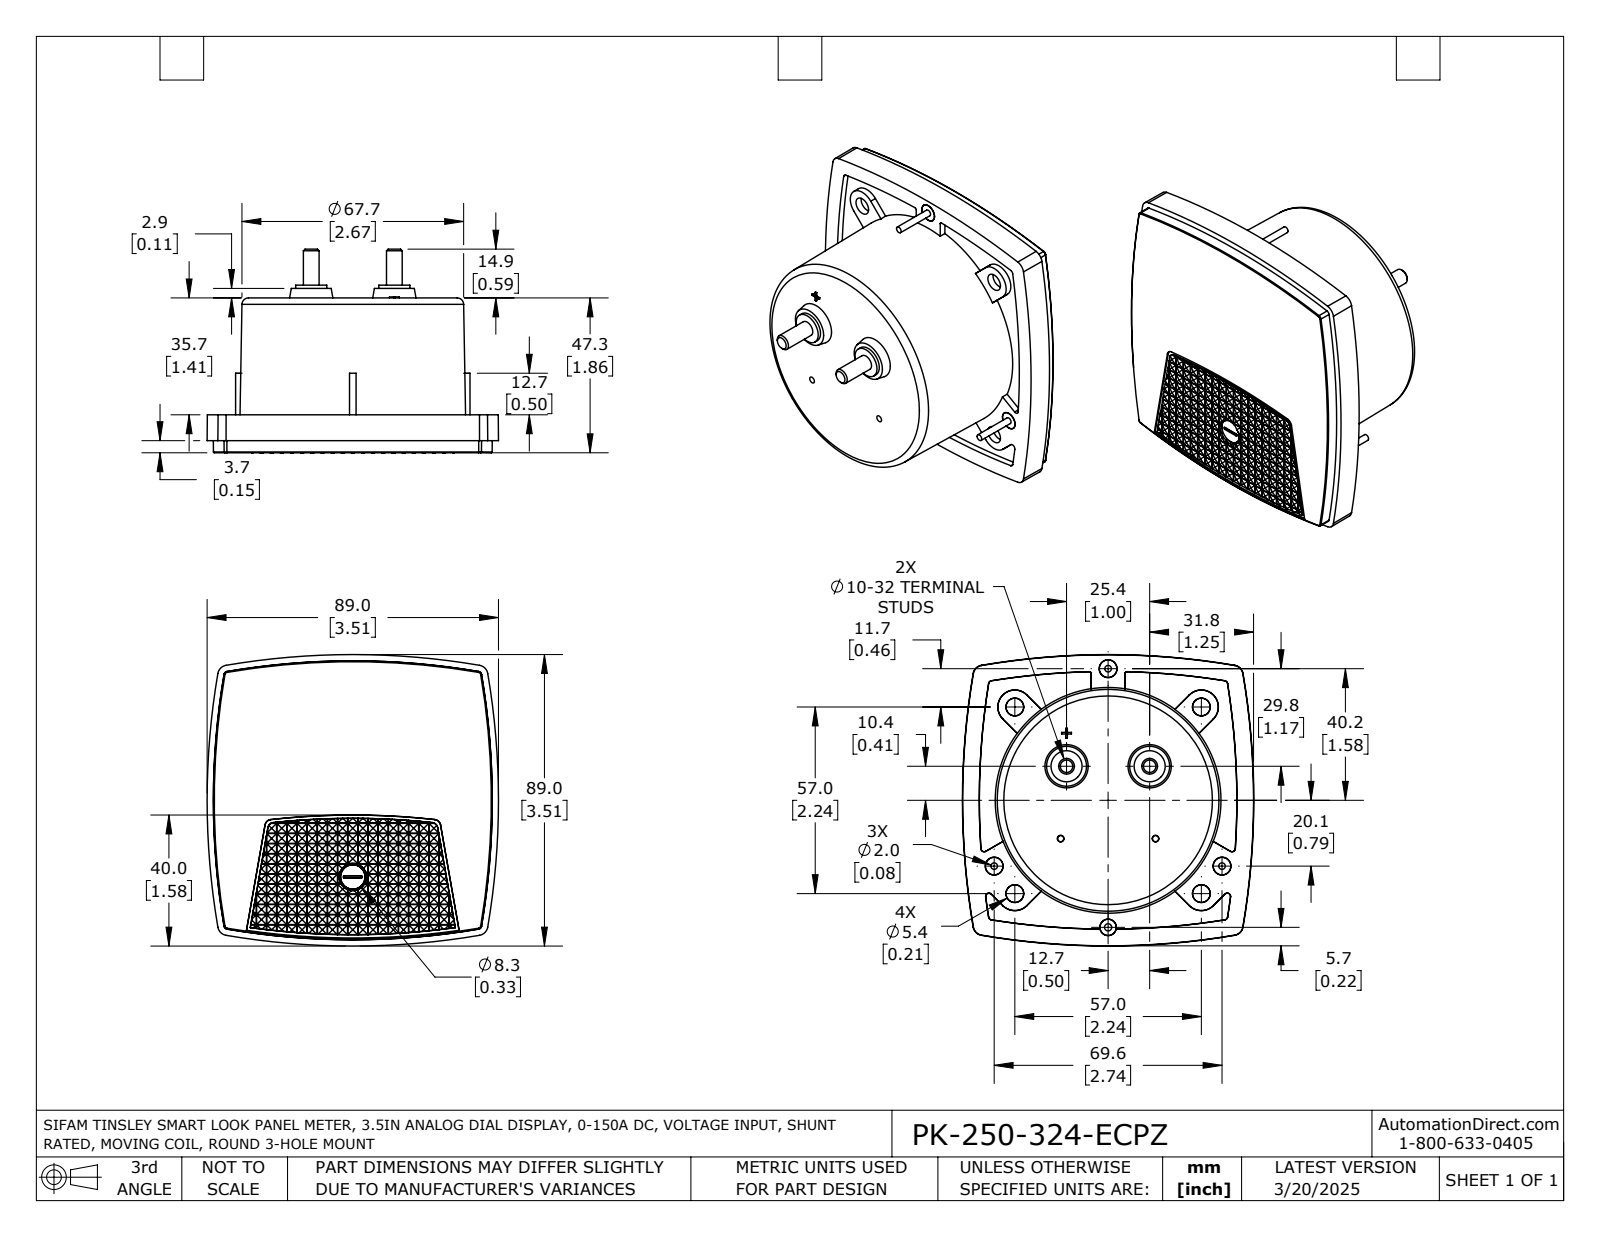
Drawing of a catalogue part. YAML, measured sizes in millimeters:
part_name: "PK-250-324-ECPZ"
step_written_by: "SolidWorks 2021 (AUTOMOTIVE_DESIGN)"
units: millimeters
bodies: {solids: 1, faces: 1078, planar: 950, cylindrical: 23, other: 105}
overall_size: [89, 89, 62.3]
volume: 212900
surface_area: 28570
round_holes:
  - {diameter: 2.2, count: 1}
round_bosses_or_shafts:
  - {diameter: 5.4, count: 3}
  - {diameter: 2, count: 3}
  - {diameter: 9.5, count: 2}
  - {diameter: 4.8, count: 2}
partial_cylinders:
  - {radius: 227.6, count: 1}
face_to_face_distances: [47.3, 35.7, 11.6, 2, 37.7, 9.6, 0.6, 2.4, 1.8, 3]
